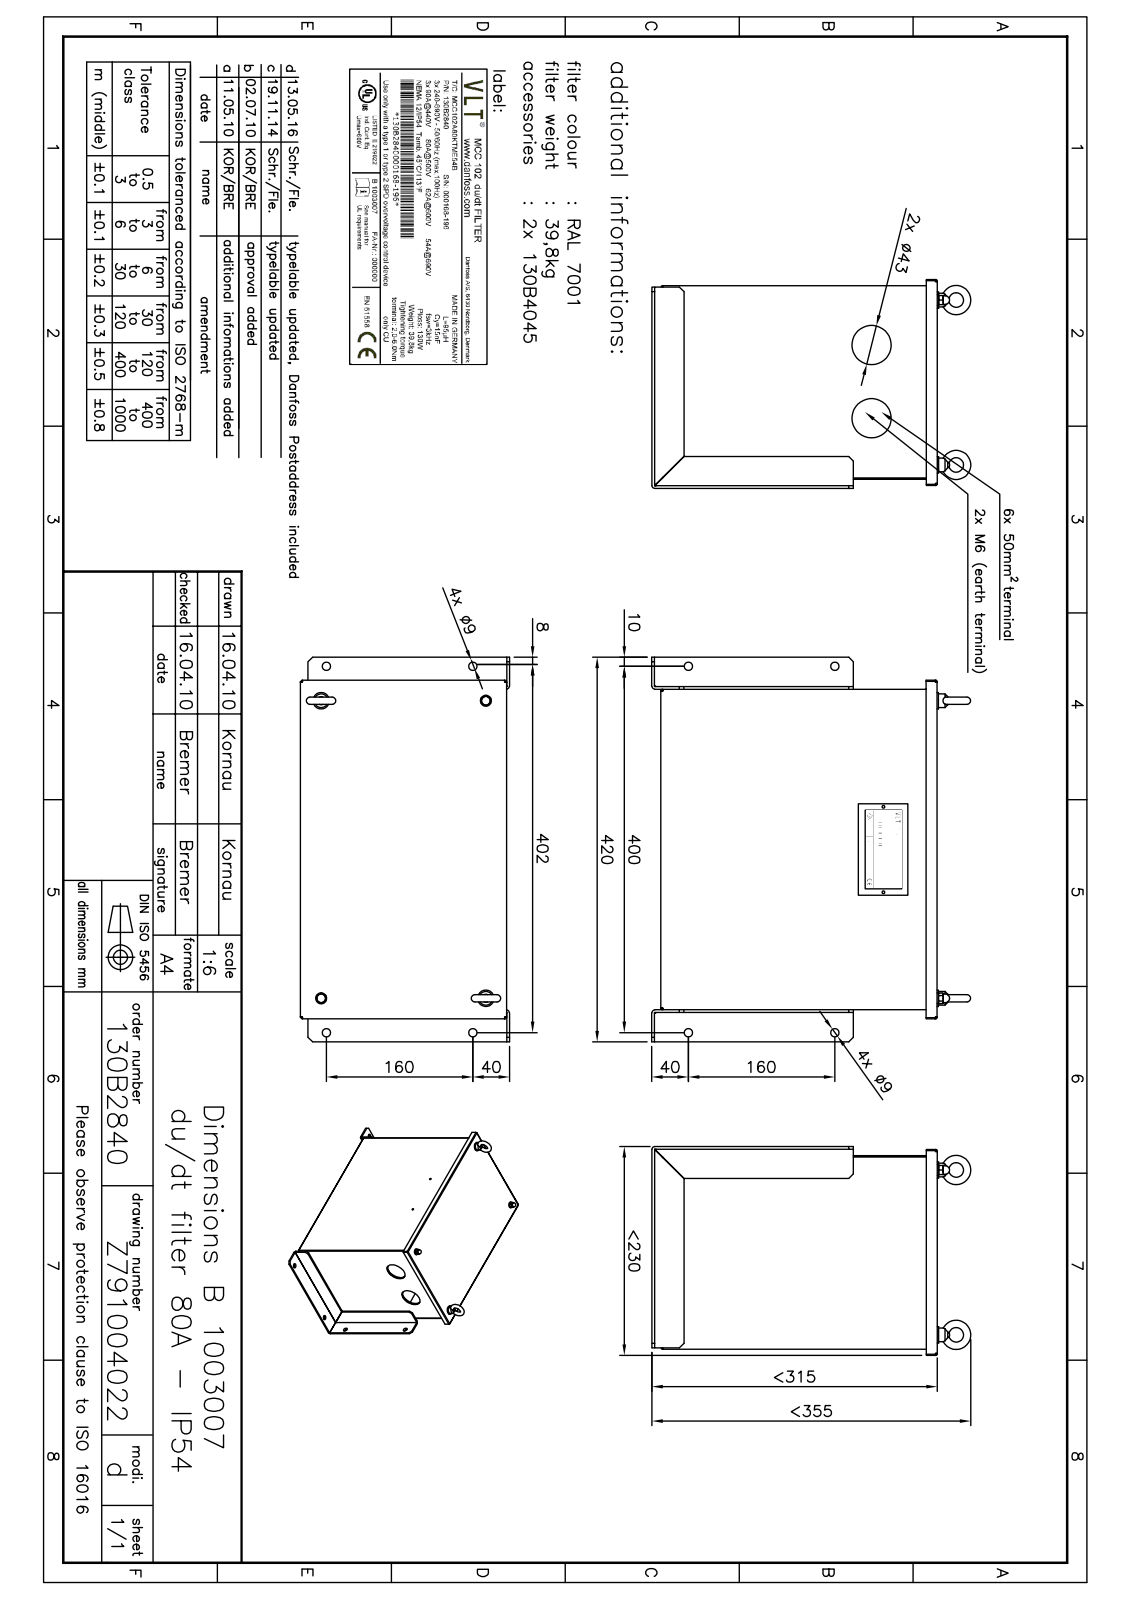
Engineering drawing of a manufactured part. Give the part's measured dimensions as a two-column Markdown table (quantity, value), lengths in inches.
| quantity | value |
| --- | --- |
| part name | 130B2840; Gehäuseschale BG 20_x IP54; Plain Washer Large_DIN_Washer DIN 9021 - 6.4; Rückwand BG 20_x IP54 (+8 more) |
| STEP written by | SolidWorks 2014 (AUTOMOTIVE_DESIGN) |
| units | inches |
| bodies | 49 solids, 1183 faces (814 planar, 241 cylindrical, 128 other) |
| overall size | 16.535 × 13.705 × 8.986 |
| volume | 840.9 in³ |
| surface area | 2 833 in² |
| round holes (diameter × count) | 0.335 × 12, 0.217 × 8, 0.354 × 8, 0.197 × 6, 0.252 × 6, 0.165 × 4, 0.236 × 4, 0.299 × 4, 0.13 × 2, 0.24 × 2, 0.281 × 2, 1.693 × 2 |
| round bosses / shafts (diameter × count) | 0.394 × 8, 0.472 × 7, 0.157 × 4, 0.709 × 2, 0.591 × 2, 0.465 × 2, 0.374 × 2, 0.335 × 2 |
| partial cylindrical surfaces (radius × count) | 0.004 × 27, 0.039 × 24, 0.063 × 16, 0.122 × 5, 0.043 × 4, 0.098 × 4, 0.276 × 4, 0.029 × 2 |
| main face-to-face distances | 0.059, 8.268, 11.752, 8.209, 13.72, 11.693, 0.118, 11.811, 8.327, 0.787 |
| hole center spacings | 0.787, 1.486, 1.575, 2.017, 2.362, 1.26, 2.677, 3.15 |
